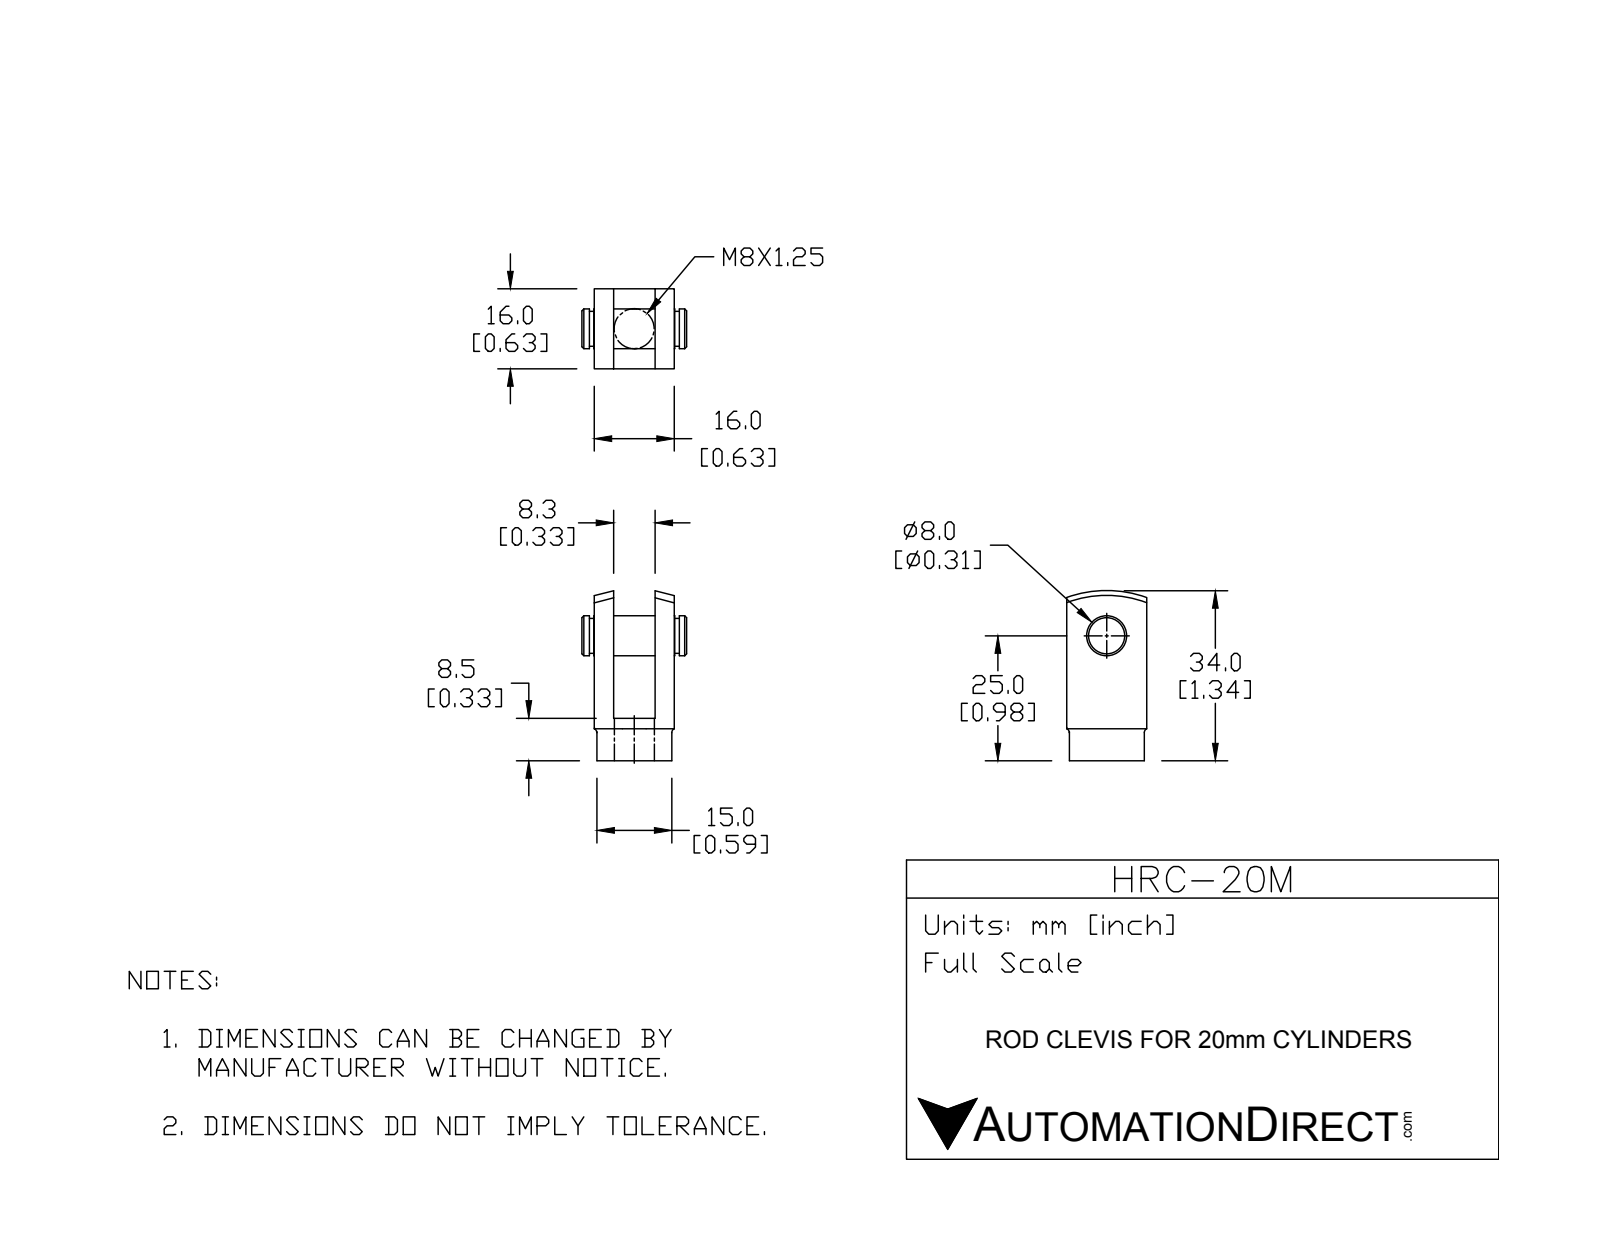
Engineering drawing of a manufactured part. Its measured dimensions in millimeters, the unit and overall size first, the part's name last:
Units: millimetres
Overall size (bounding box): 34 × 21 × 16
Round holes (diameter × count): ⌀6.8 ×1
Round bosses / shafts (diameter × count): ⌀15 ×1, ⌀8 ×1, ⌀7 ×1
Main face-to-face distances: 3.85, 12.15, 16, 8.3, 8.5, 2.5, 6.35, 14.65, 18.5, 6.38
Volume: 5 028 mm³ · Surface area: 3 617 mm²
Bodies: 2 solids, 54 faces (18 planar, 18 cylindrical, 18 other)
Part name (STEP PRODUCT): HRC-20M
STEP written by: SolidWorks 2015 (CONFIG_CONTROL_DESIGN)
